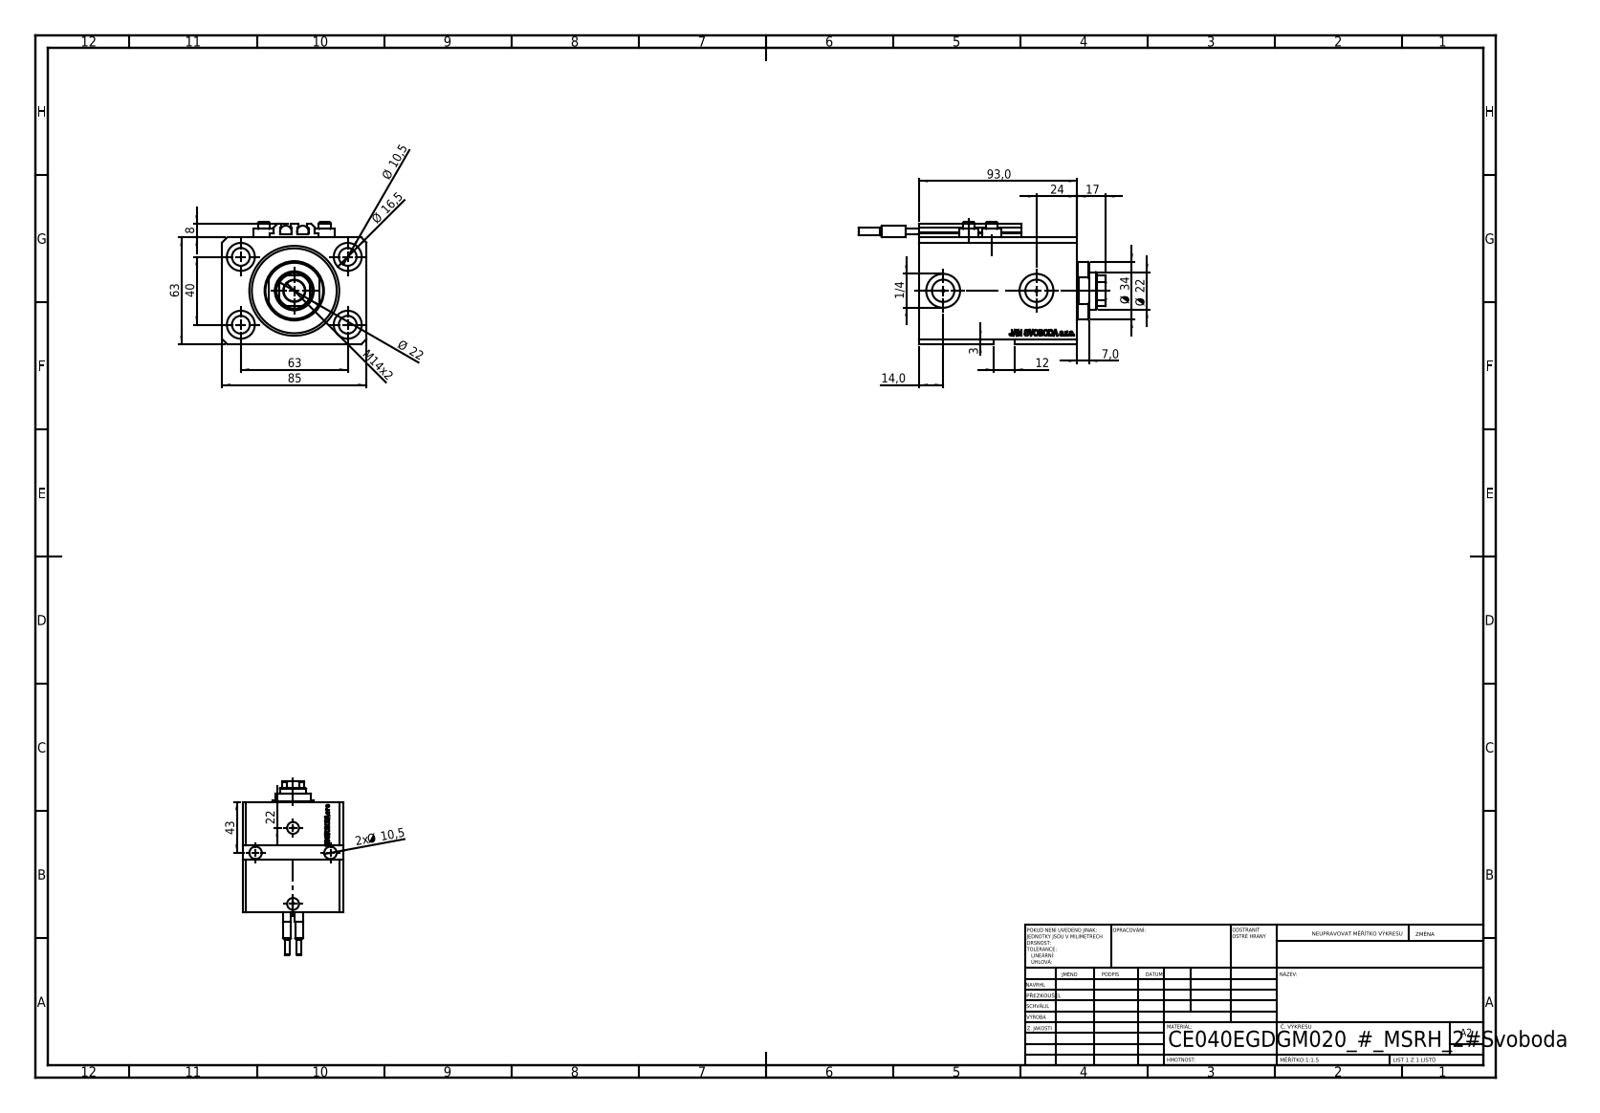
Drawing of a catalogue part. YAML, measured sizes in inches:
part_name: "V250CE_E_Body; ALLEN BOLT V250CE; SWITCH_V250CE; V250CE_C_VCP (+1 more)"
step_written_by: "SolidWorks 2019 (CONFIG_CONTROL_DESIGN)"
units: inches
bodies: {solids: 10, faces: 1155, planar: 571, cylindrical: 150, other: 434}
overall_size: [5.748, 3.346, 2.835]
volume: 26.68
surface_area: 154.5
round_holes:
  - {diameter: 0.413, count: 6}
  - {diameter: 0.049, count: 4}
  - {diameter: 0.157, count: 4}
  - {diameter: 0.65, count: 4}
  - {diameter: 0.394, count: 2}
  - {diameter: 0.518, count: 2}
  - {diameter: 0.787, count: 2}
  - {diameter: 0.492, count: 1}
  - {diameter: 0.866, count: 1}
  - {diameter: 1.575, count: 1}
  - {diameter: 2.087, count: 1}
round_bosses_or_shafts:
  - {diameter: 0.457, count: 4}
  - {diameter: 0.276, count: 4}
  - {diameter: 0.268, count: 2}
  - {diameter: 0.256, count: 2}
  - {diameter: 0.157, count: 2}
  - {diameter: 1.339, count: 1}
partial_cylinders:
  - {radius: 0.008, count: 10}
  - {radius: 0.413, count: 1}
face_to_face_distances: [2.48, 3.346, 3.661, 0.669, 2.992, 0.449, 2.543, 3.213, 0.118, 2.559]
hole_center_spacings: [1.469, 2.48, 0.535, 0.606, 0.983, 1.103, 1.119, 1.324]
